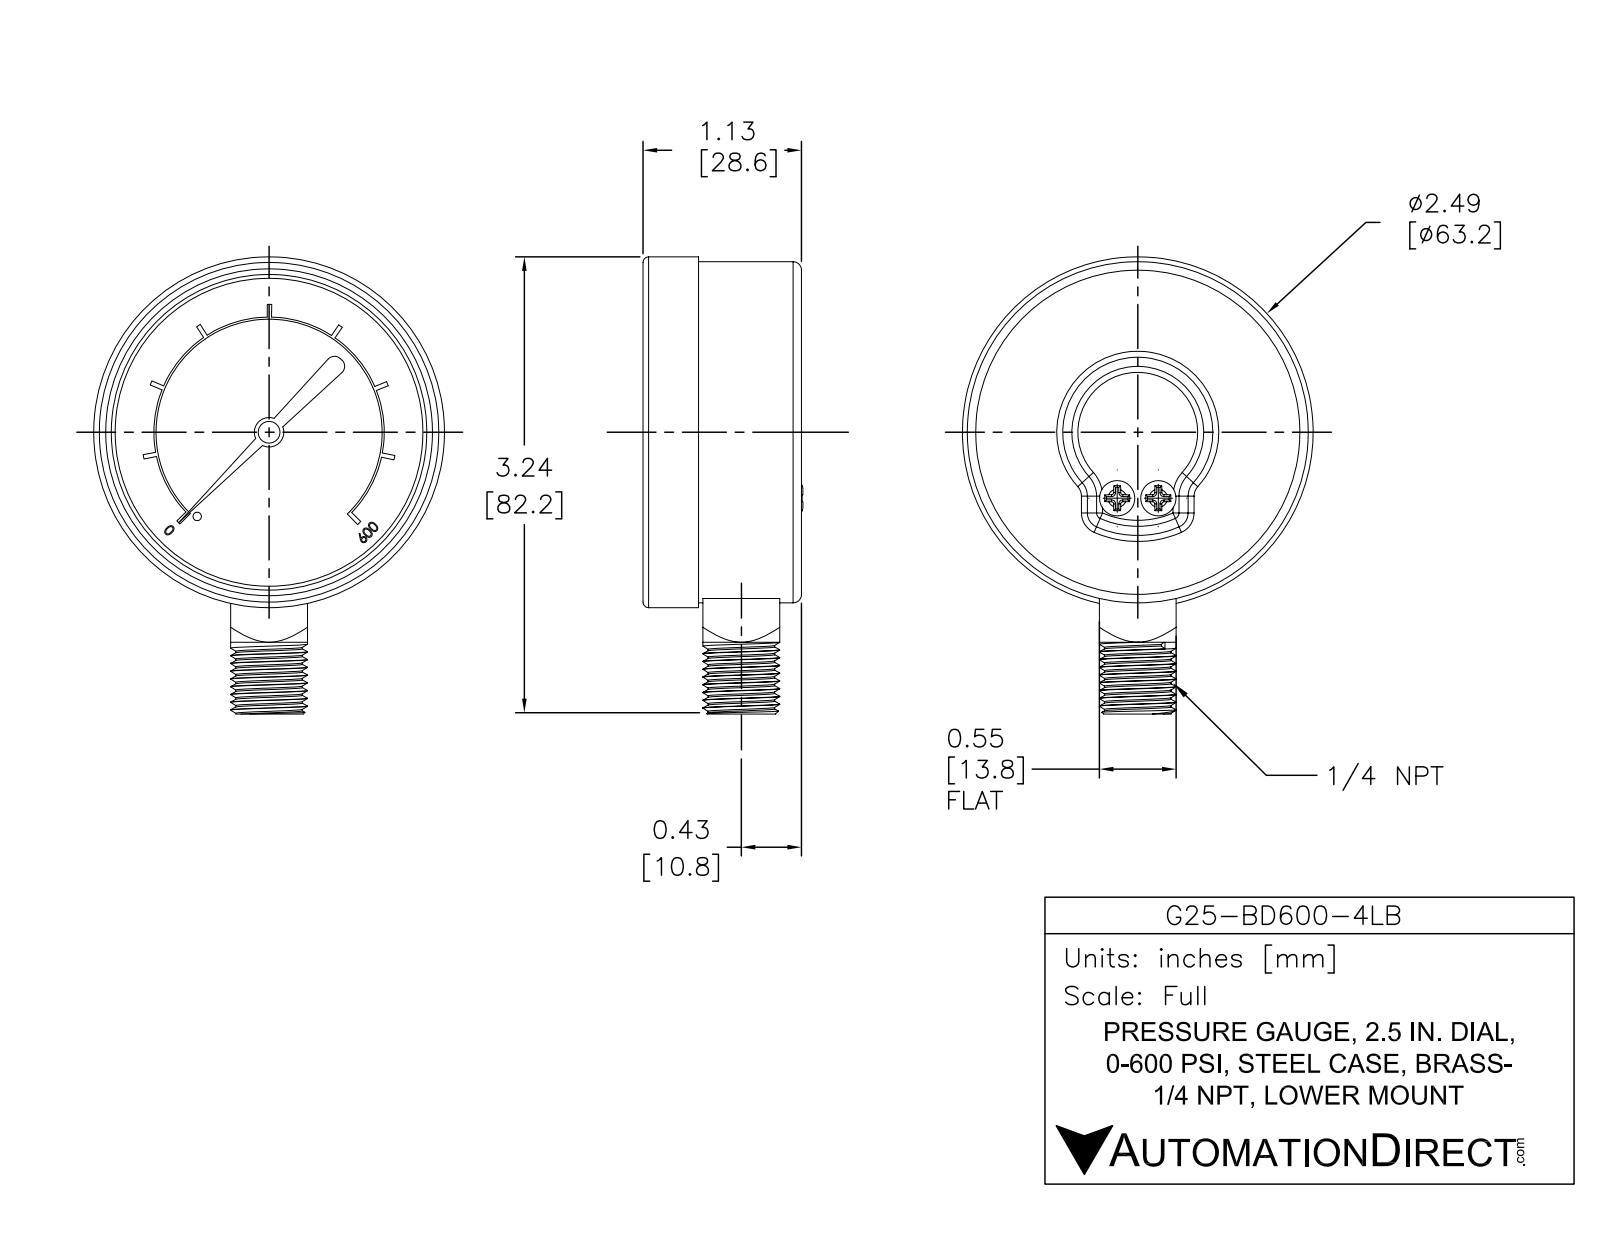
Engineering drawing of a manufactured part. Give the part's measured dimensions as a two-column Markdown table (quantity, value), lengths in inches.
| quantity | value |
| --- | --- |
| part name | G25-BD600-4LB |
| STEP written by | SolidWorks 2021 (AUTOMOTIVE_DESIGN) |
| units | inches |
| bodies | 1 solid, 221 faces (113 planar, 35 cylindrical, 73 other) |
| overall size | 3.245 × 2.49 × 1.135 |
| volume | 4.288 in³ |
| surface area | 22.39 in² |
| round holes (diameter × count) | 0.14 × 1, 2.185 × 1 |
| round bosses / shafts (diameter × count) | 0.25 × 2, 2.49 × 1, 2.421 × 1, 0.545 × 1, 0.154 × 1, 0.123 × 1, 0.06 × 1 |
| partial cylindrical surfaces (radius × count) | 0.06 × 6, 0.105 × 1, 0.803 × 1, 0.818 × 1 |
| main face-to-face distances | 0.835, 0.1, 0.735, 1.125, 1.025, 0.29, 0.545, 0.731, 0.631, 0.104 |
